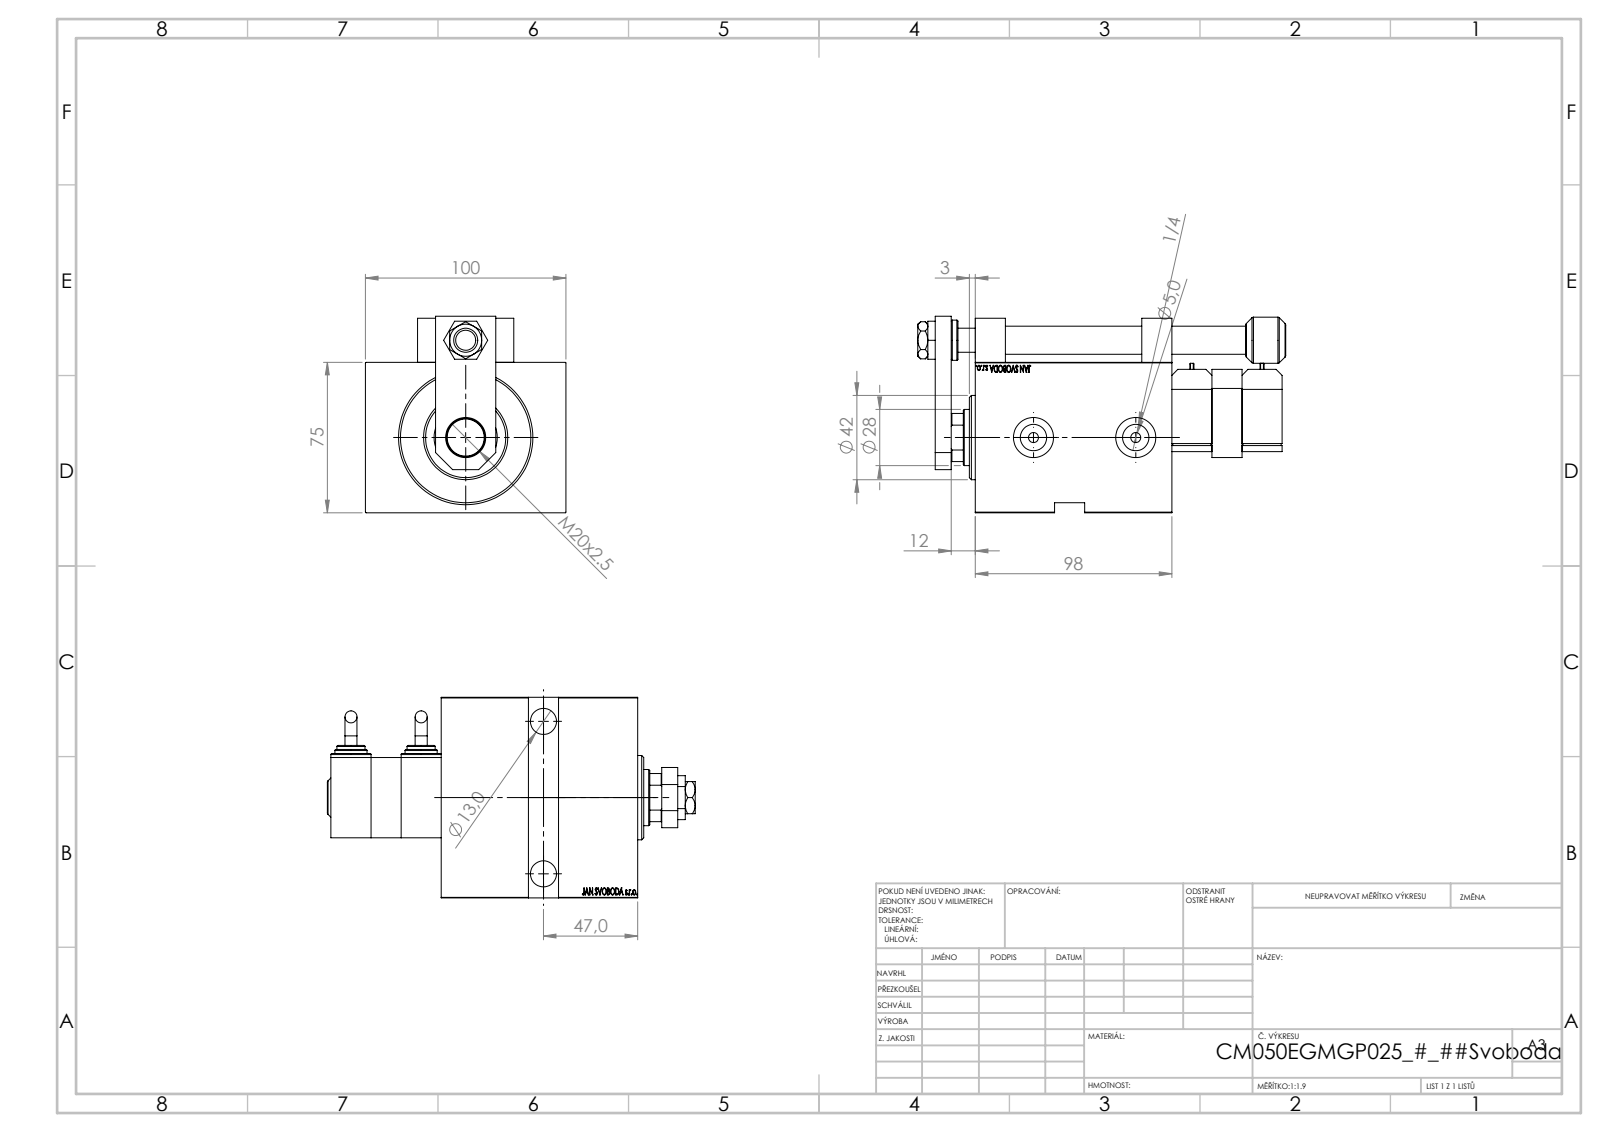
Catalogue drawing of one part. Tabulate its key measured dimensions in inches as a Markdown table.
| quantity | value |
| --- | --- |
| part name | NUT_D16; NUT_D19_P; KROUZEK_PRO_TYC; TYC_P (+7 more) |
| STEP written by | SolidWorks 2019 (CONFIG_CONTROL_DESIGN) |
| units | inches |
| bodies | 14 solids, 1073 faces (522 planar, 102 cylindrical, 449 other) |
| overall size | 7.224 × 3.937 × 3.858 |
| volume | 51.19 in³ |
| surface area | 227.9 in² |
| round holes (diameter × count) | 0.157 × 4, 0.315 × 4, 0.512 × 3, 0.787 × 3, 0.197 × 2, 0.518 × 2, 0.748 × 2, 0.472 × 1, 0.551 × 1, 0.728 × 1, 1.102 × 1, 1.24 × 1 |
| round bosses / shafts (diameter × count) | 0.787 × 3, 0.63 × 2, 0.551 × 2, 0.236 × 2, 2.047 × 1, 1.654 × 1, 0.906 × 1 |
| partial cylindrical surfaces (radius × count) | 0.118 × 1, 0.531 × 1 |
| main face-to-face distances | 1.378, 2.953, 3.937, 3.858, 0.787, 4.646, 0.591, 0.197, 2.756, 1.181 |
| hole center spacings | 0.787, 1.906, 2.037, 2.447, 2.55, 3.268, 3.361, 1.909 |
